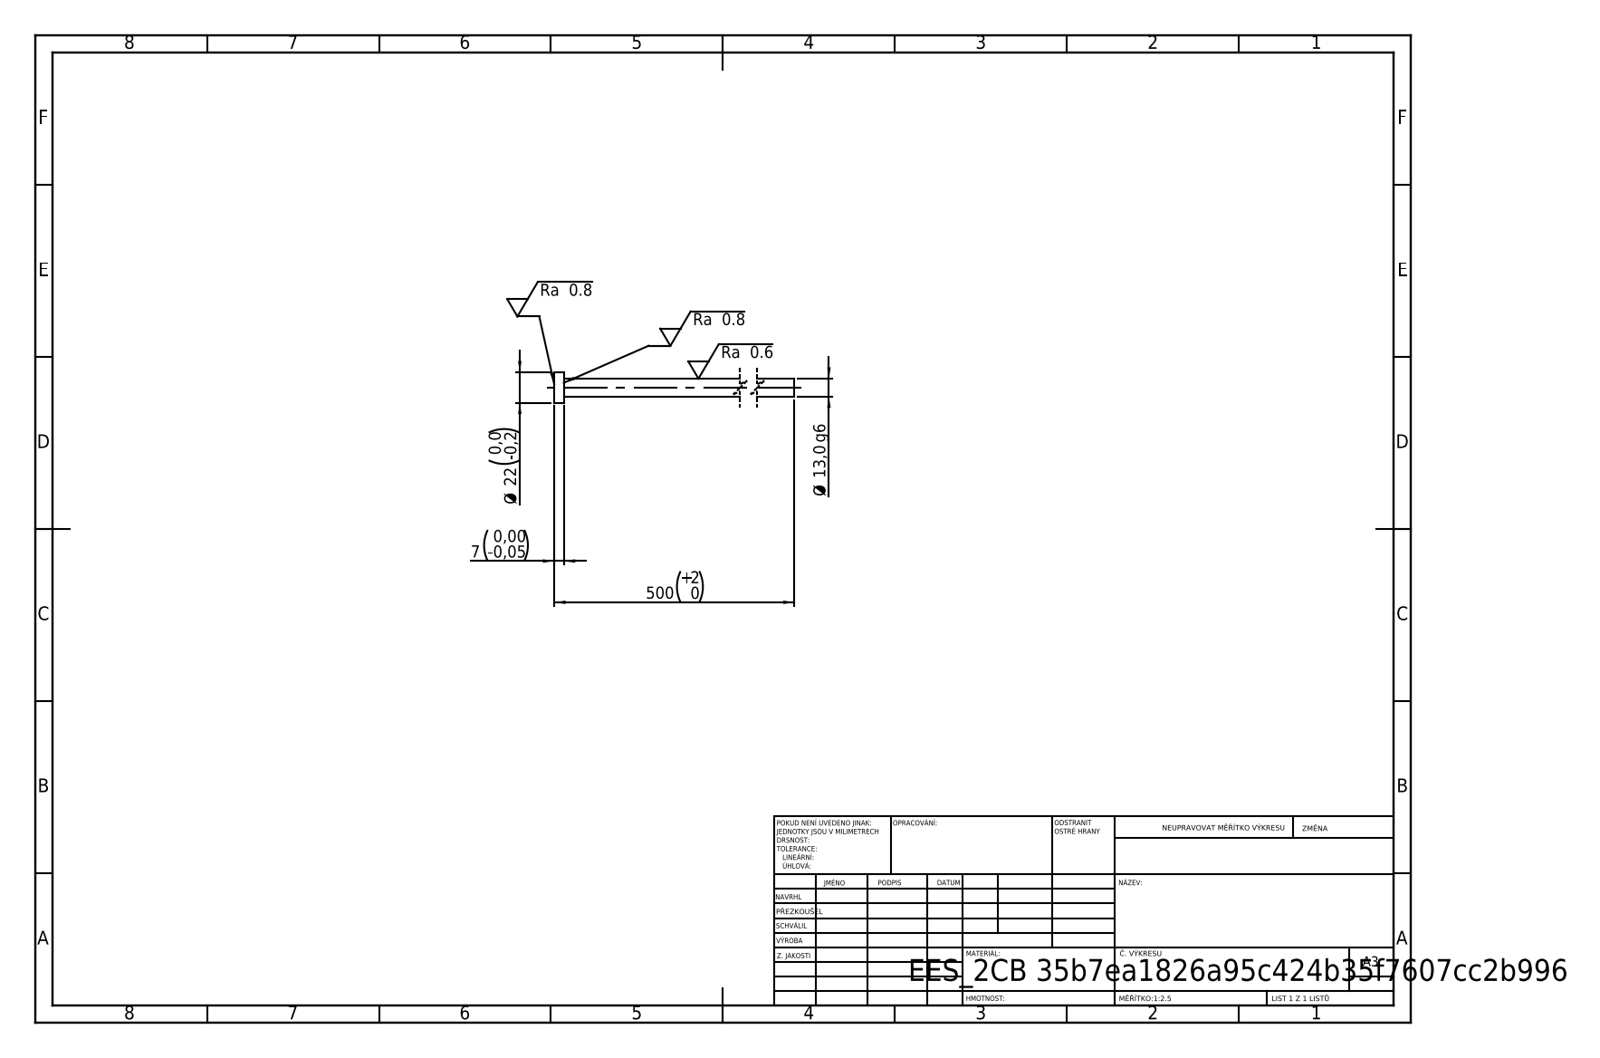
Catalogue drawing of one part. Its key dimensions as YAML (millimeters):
step_written_by: "SolidWorks 2019 (CONFIG_CONTROL_DESIGN)"
units: millimeters
bodies: {solids: 1, faces: 7, planar: 3, cylindrical: 4, other: 0}
overall_size: [500, 22, 22]
volume: 68098
surface_area: 21379
round_bosses_or_shafts:
  - {diameter: 22, count: 1}
  - {diameter: 13, count: 1}
face_to_face_distances: [7, 500, 493]
